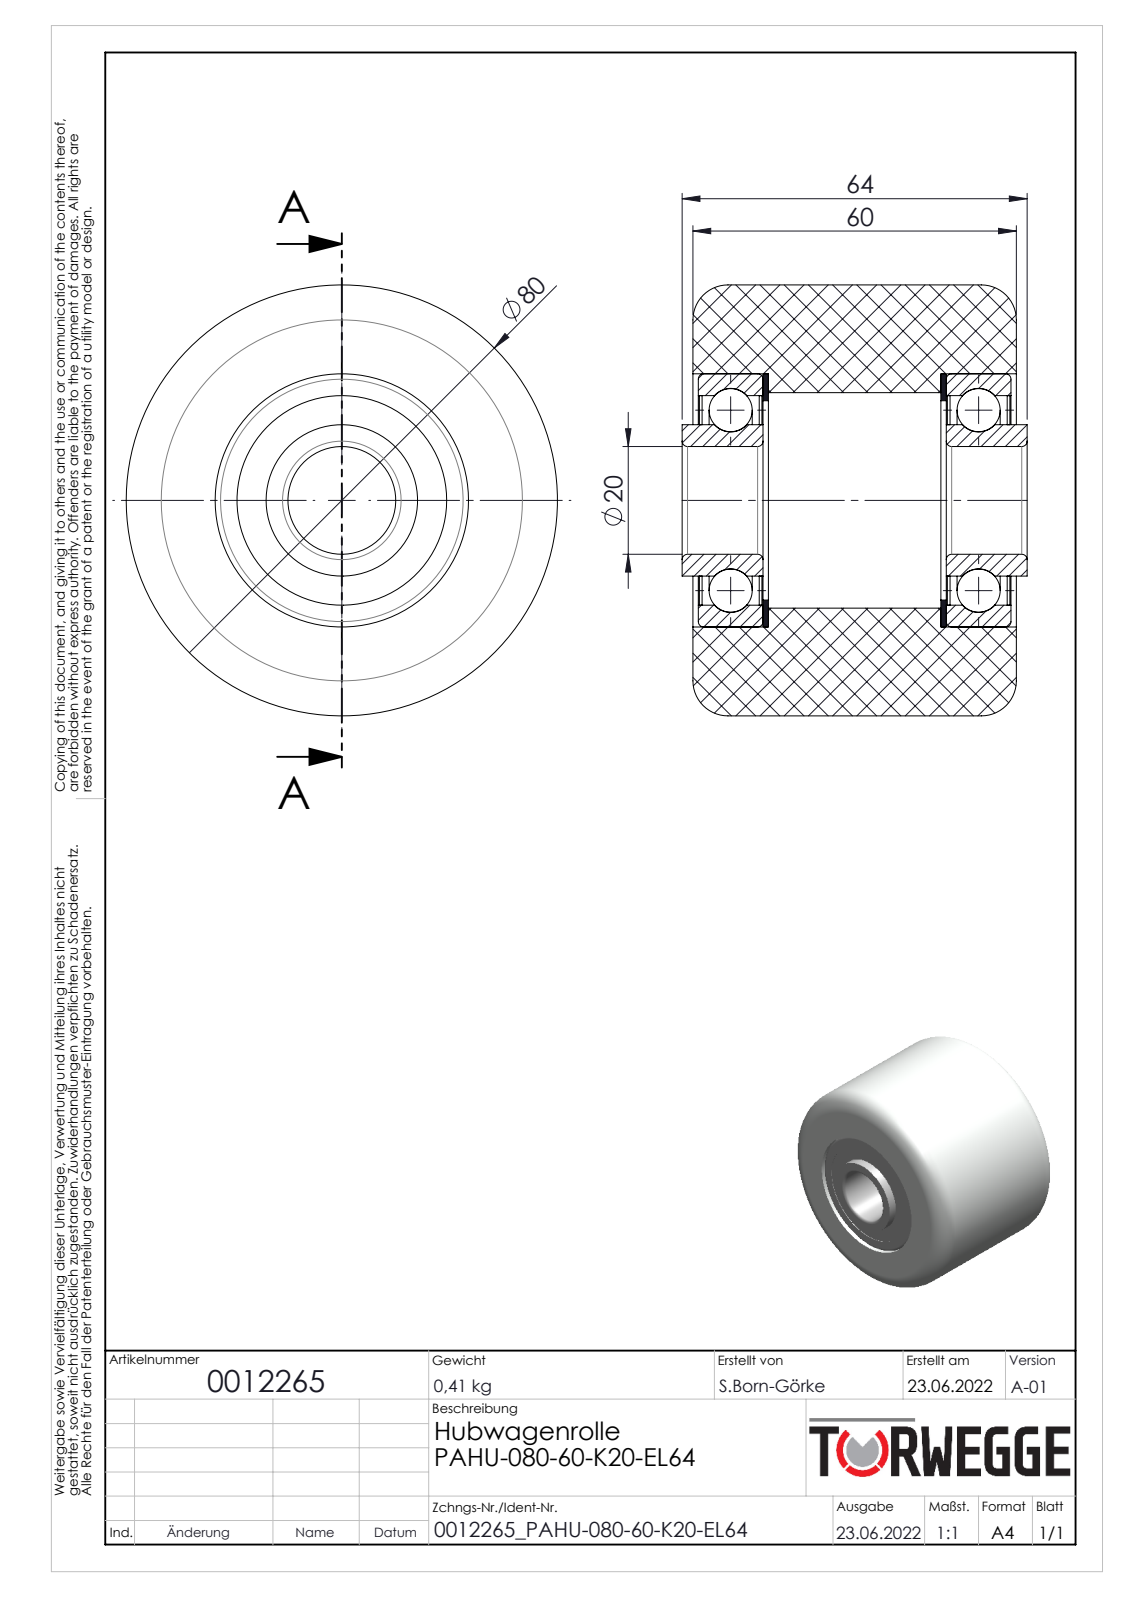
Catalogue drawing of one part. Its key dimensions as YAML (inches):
part_name: "0012265"
step_written_by: "SolidWorks 2020 (AUTOMOTIVE_DESIGN)"
units: inches
bodies: {solids: 13, faces: 128, planar: 24, cylindrical: 56, other: 48}
overall_size: [3.15, 3.15, 2.52]
volume: 14.72
surface_area: 88.47
round_holes:
  - {diameter: 0.787, count: 1}
  - {diameter: 1.106, count: 1}
  - {diameter: 1.457, count: 1}
  - {diameter: 1.531, count: 1}
  - {diameter: 1.575, count: 1}
round_bosses_or_shafts:
  - {diameter: 3.15, count: 1}
  - {diameter: 1.85, count: 1}
face_to_face_distances: [1.811, 0.512, 0.039, 1.85, 0.047, 0.067, 0.484, 0.504, 0.02, 0.437]
